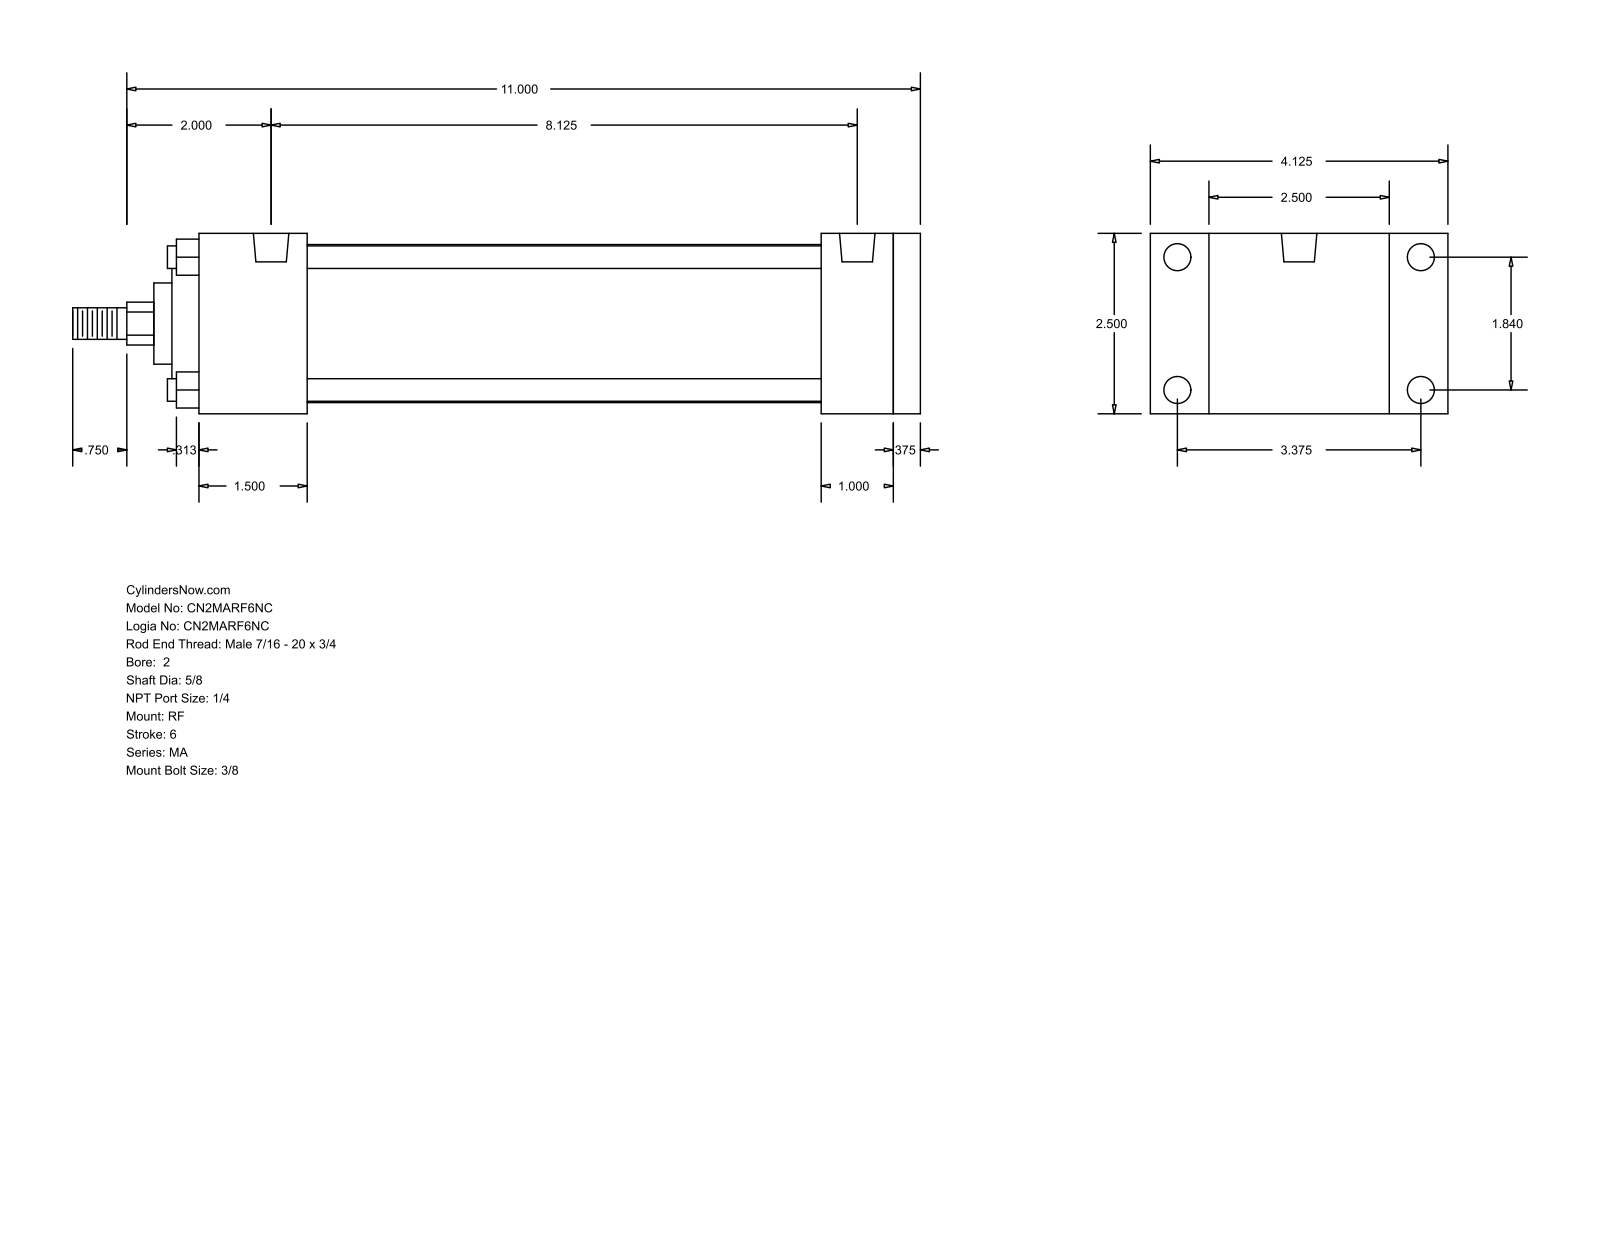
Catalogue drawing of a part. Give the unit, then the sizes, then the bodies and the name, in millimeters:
Units: millimetres
Overall size (bounding box): 298.45 × 104.78 × 63.5
Round holes (diameter × count): ⌀7.94 ×4, ⌀9.53 ×4, ⌀12.49 ×2
Round bosses / shafts (diameter × count): ⌀7.94 ×4, ⌀55.63 ×1, ⌀50.8 ×1, ⌀28.57 ×1, ⌀15.88 ×1, ⌀11.11 ×1
Partial cylindrical surfaces — rounded edges, fillets, slot ends (radius × count): R7.54 ×1
Main face-to-face distances: 63.5, 9.52, 254, 38.1, 34.93, 263.52, 244.48, 206.38, 215.9, 219.07
Hole centre spacings: 46.74, 85.72, 97.63, 206.38
Bodies: 0 solids, 94 faces (65 planar, 29 cylindrical, 0 other)
Part name (STEP PRODUCT): MA_RF__0200_0.625
STEP written by: GSSL Pune (CONFIG_CONTROL_DESIGN)
